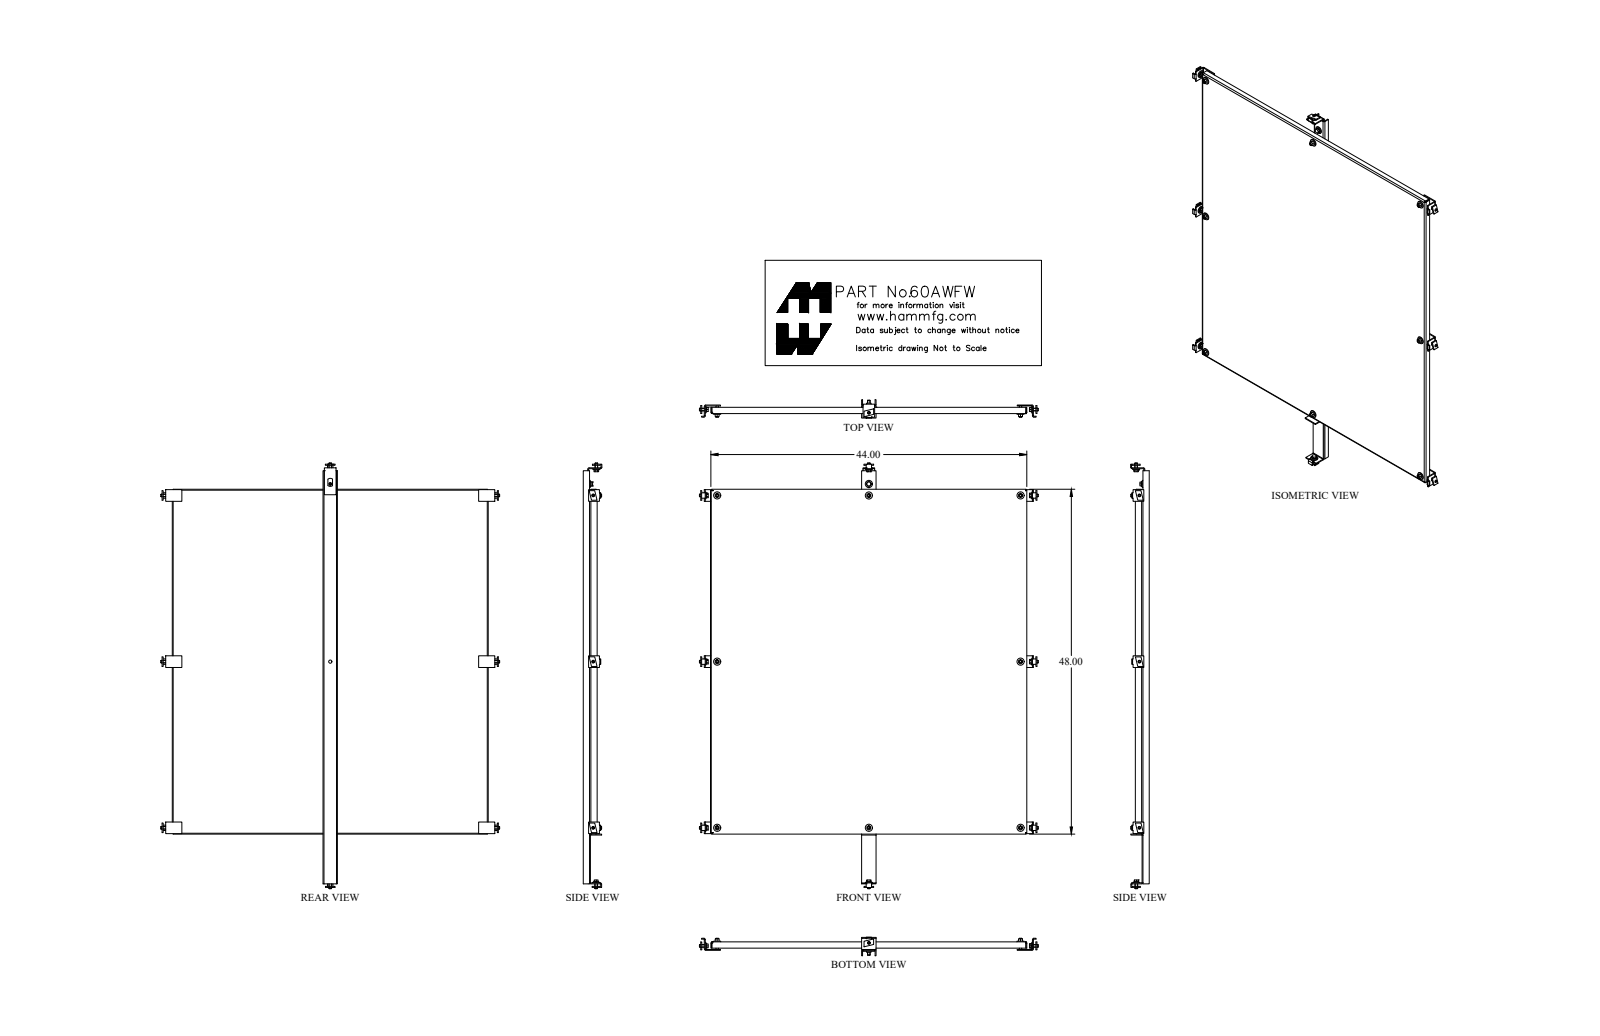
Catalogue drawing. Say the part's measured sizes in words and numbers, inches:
The part is named "60AWFW_Default". Its 3-D file was written by "SolidWorks 2018 (CONFIG_CONTROL_DESIGN)". It is 1 solid with 70 faces: 38 planar, 24 cylindrical and 8 other. Overall it measures 48 by 44 by 0.875 inches. Its volume is 279.7 cubic inches and its surface area 4 501 square inches. Round holes: 8 of diameter 0.563. Partial cylindrical surfaces (rounded edges, fillets, slot ends): 4 of radius 0.06, 4 of radius 0.185. The main face-to-face distances are 0.125, 43.875, 0.125, 47.875, 44, 43.75, 47.75, 48, 0.875, 0.75. The hole center spacings are 21.125, 23.125, 31.321, 48.164, 50.846, 42.25, 46.25, 62.643.
